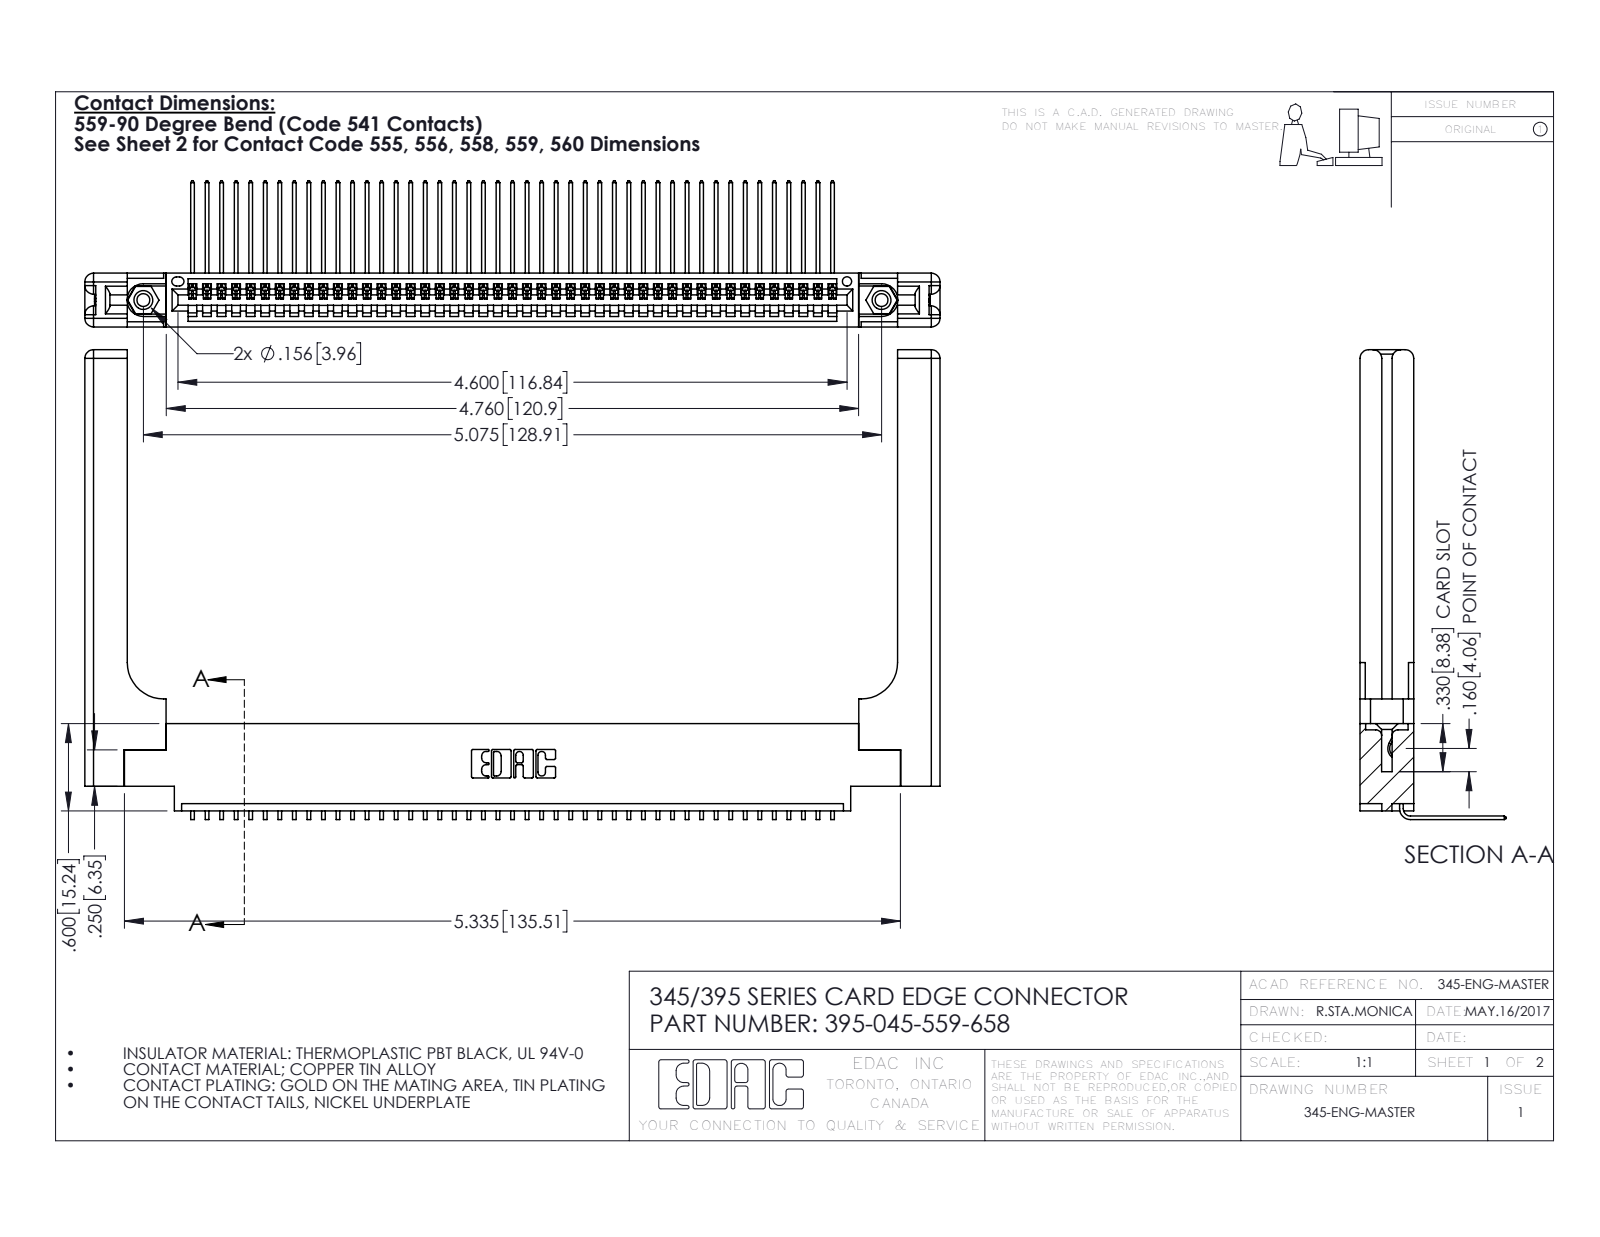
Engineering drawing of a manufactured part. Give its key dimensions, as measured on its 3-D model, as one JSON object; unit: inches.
{"part_name": "395-045-559-658; 345-292-001_558 559 Tail - 1; 345 Part_0.170 Offset - 0.156 Dia-TH; 345-220-058_345-220-058 (+1 more)", "step_written_by": "SolidWorks 2016 (CONFIG_CONTROL_DESIGN)", "units": "inches", "bodies": {"solids": 50, "faces": 3086, "planar": 2122, "cylindrical": 904, "other": 60}, "overall_size": [5.879, 3.229, 1.005], "volume_in3": 1.388, "surface_area_in2": 39.19, "round_holes": [[0.089, 2], [0.125, 2], [0.156, 2], [0.064, 1]], "round_bosses_or_shafts": [[0.155, 2]], "partial_cylinders_radius": [[0.006, 90], [0.01, 22], [0.06, 16], [0.007, 6], [0.031, 6], [0.026, 3], [0.03, 2], [0.031, 2]], "face_to_face_distances": [0.37, 0.072, 0.298, 0.098, 0.272, 0.025, 0.2, 0.225, 0.148, 0.15], "hole_center_spacings": [0.27, 4.839, 5.075]}
